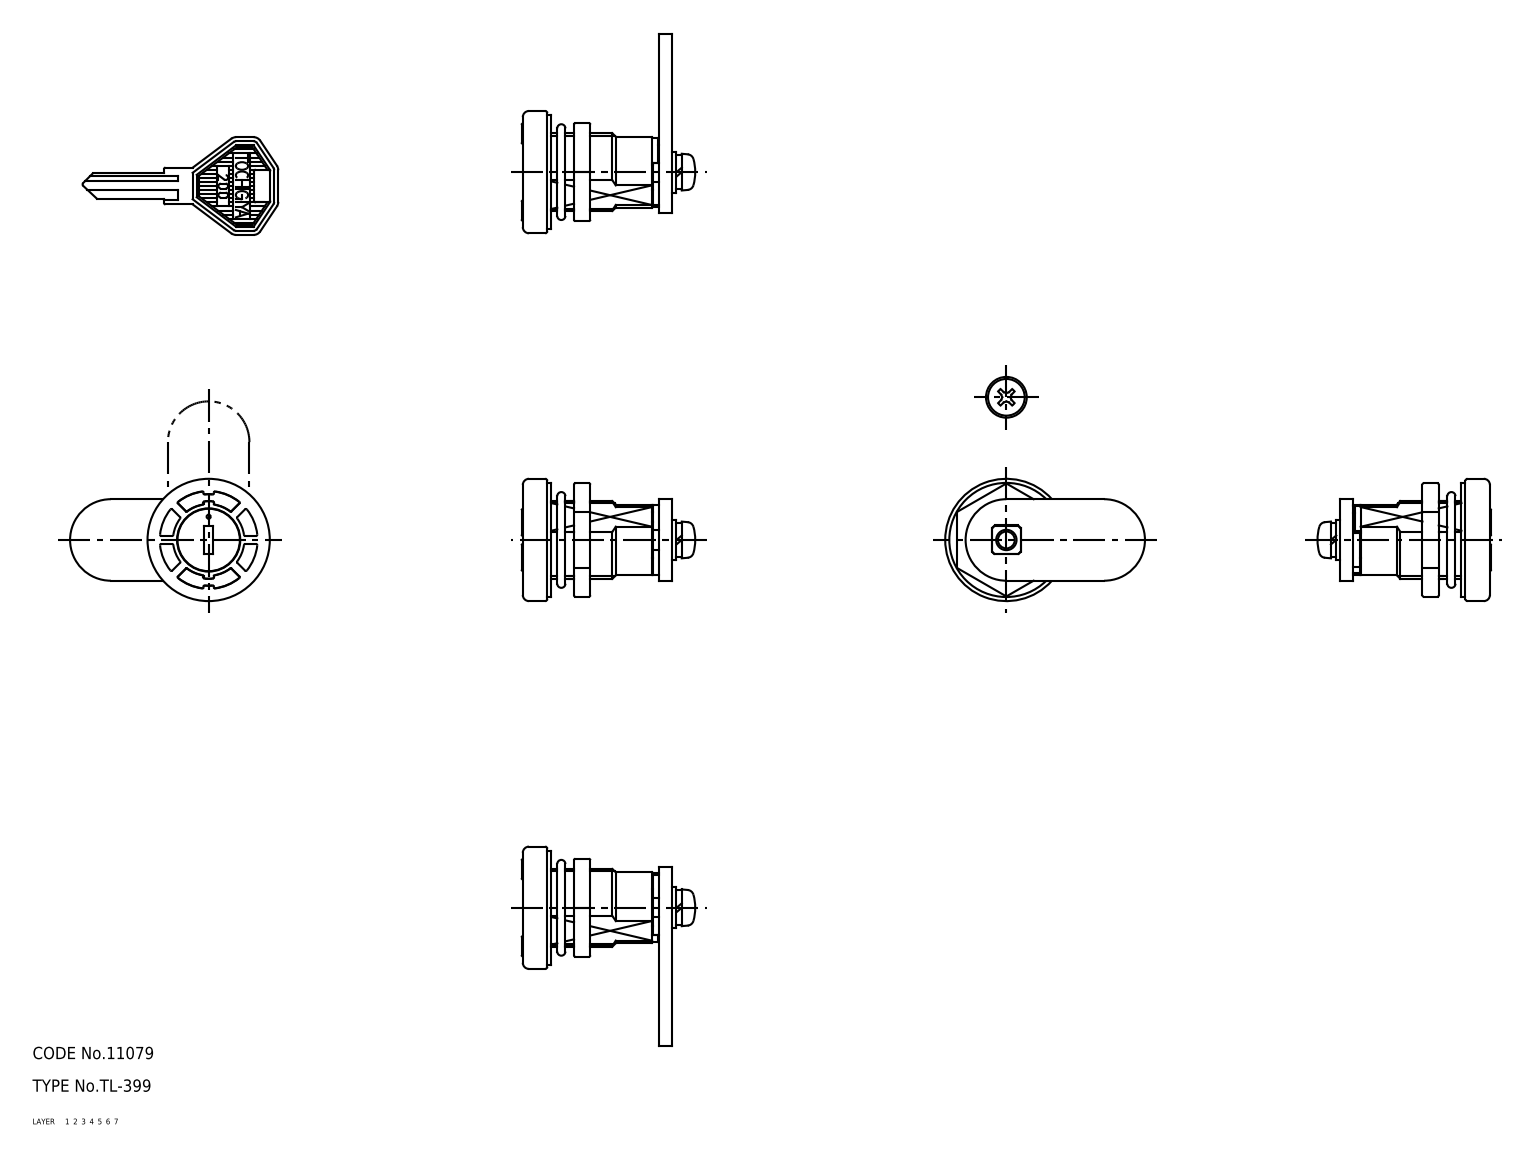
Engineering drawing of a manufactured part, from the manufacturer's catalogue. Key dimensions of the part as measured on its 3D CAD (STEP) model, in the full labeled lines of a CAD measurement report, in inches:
Part name (STEP PRODUCT): key; washer; nut; TL_399 (+3 more)
STEP written by: SolidWorks 2015 (AUTOMOTIVE_DESIGN)
Units: inches
Bodies: 6 solids, 267 faces (130 planar, 106 cylindrical, 31 other)
Overall size (bounding box): 4.145 × 1.929 × 1.181
Volume: 0.986 in³ · Surface area: 14.06 in²
Round holes (diameter × count): ⌀0.039 ×1, ⌀0.197 ×1, ⌀0.61 ×1
Round bosses / shafts (diameter × count): ⌀1.181 ×1, ⌀1.102 ×1, ⌀0.748 ×1, ⌀0.602 ×1, ⌀0.394 ×1, ⌀0.354 ×1, ⌀0.335 ×1
Partial cylindrical surfaces — rounded edges, fillets, slot ends (radius × count): R0.02 ×23, R0.079 ×6, R0.012 ×2, R0.394 ×2, R0.179 ×1, R0.266 ×1, R0.276 ×1, R0.335 ×1
Main face-to-face distances: 0.126, 0.079, 1.445, 1.319, 0.276, 1.169, 1.043, 0.63, 0.157, 0.295
Hole centre spacings: 0.224
